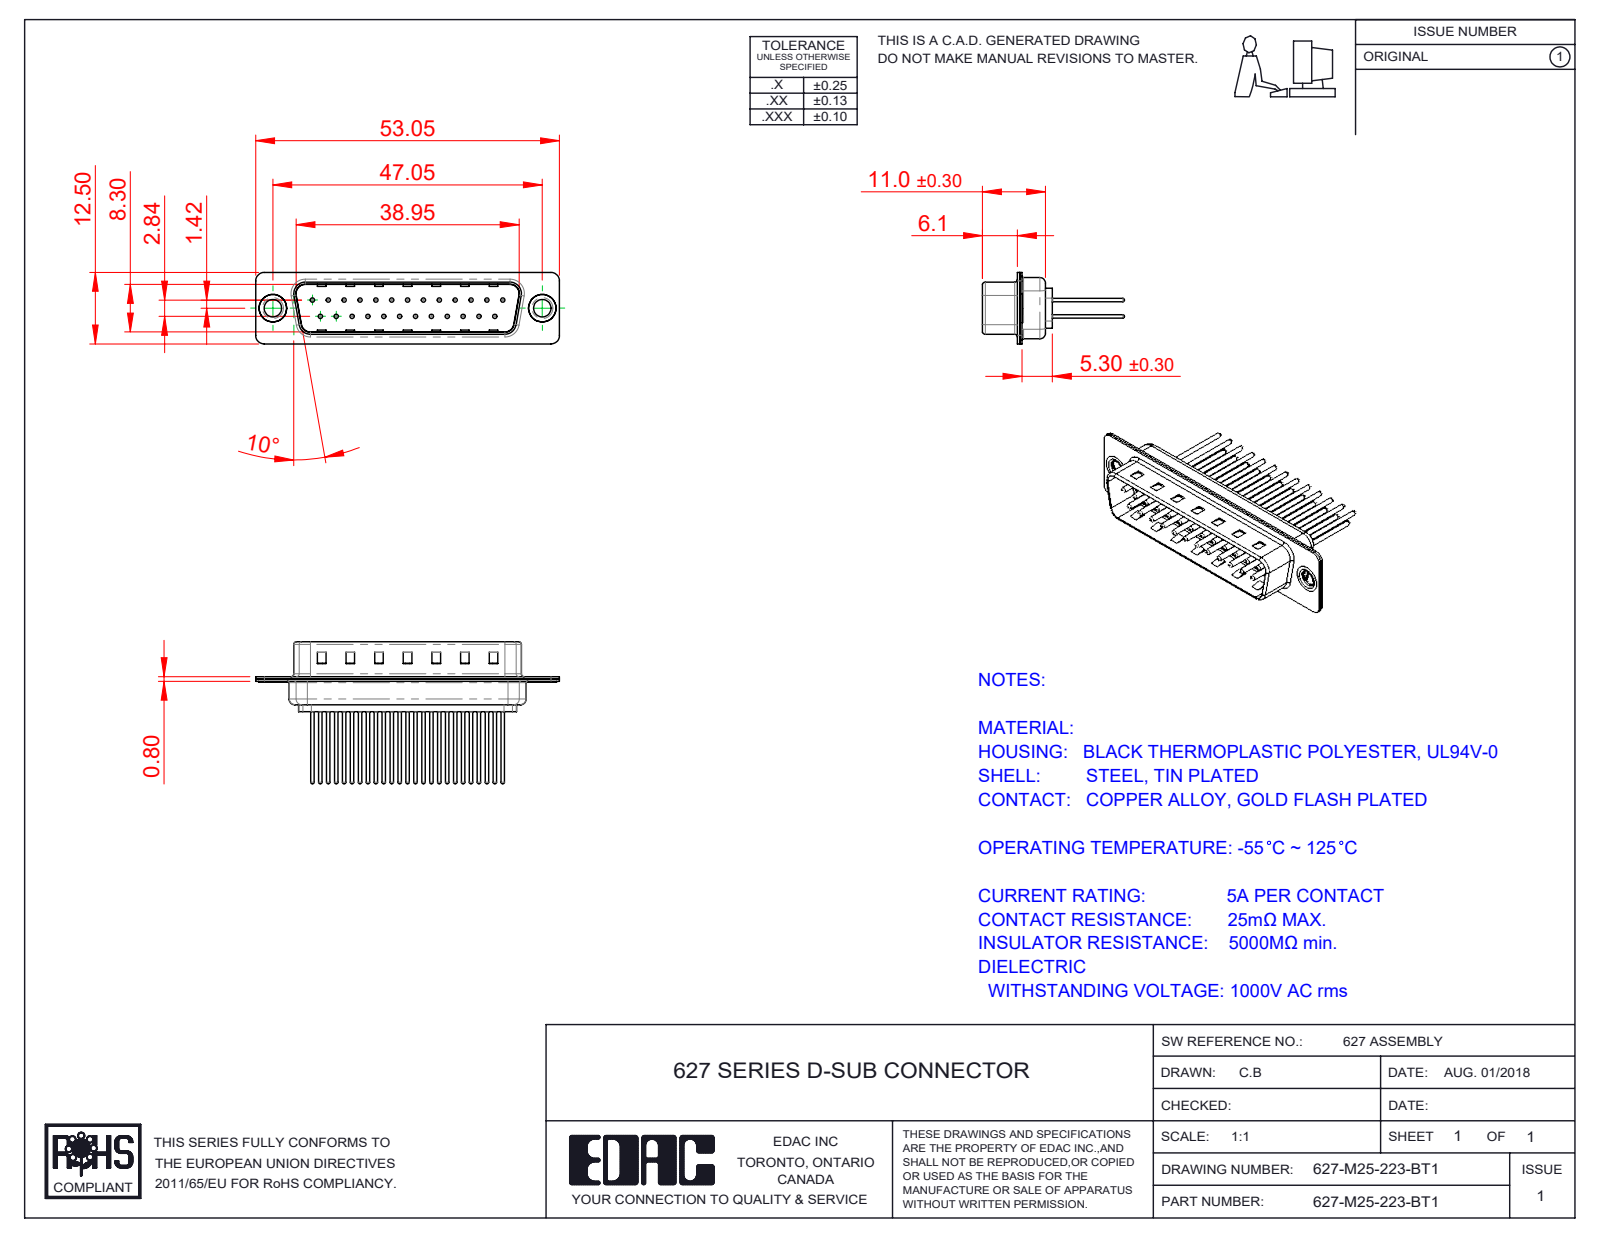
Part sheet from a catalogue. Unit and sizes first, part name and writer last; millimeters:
Units: millimetres
Overall size (bounding box): 53.05 × 24.77 × 12.5
Round holes (diameter × count): ⌀0.75 ×25, ⌀1.6 ×25, ⌀2 ×25, ⌀3.05 ×2, ⌀4 ×2, ⌀4.8 ×2
Round bosses / shafts (diameter × count): ⌀1.5 ×25, ⌀0.6 ×25, ⌀5 ×2, ⌀4.9 ×2, ⌀3.55 ×2
Partial cylindrical surfaces — rounded edges, fillets, slot ends (radius × count): R1.5 ×16, R2 ×12, R0.5 ×8, R1.6 ×8, R0.25 ×4, R0.6 ×4, R0.65 ×4, R0.9 ×4
Main face-to-face distances: 0.4, 0.8, 9.5, 9.1, 8.7, 9.9, 1.2, 6.1, 5.7, 0.75
Hole centre spacings: 3.16, 2.77, 5.54, 8.31, 11.08, 13.85, 16.62, 5.03
Volume: 2 690 mm³ · Surface area: 7 022 mm²
Bodies: 30 solids, 1275 faces (346 planar, 471 cylindrical, 458 other)
Part name (STEP PRODUCT): 627M Contact Row 1_23; 627-M25-223-BT1; 627M Shell Rear_25 Contacts; 627M Thru Hole Rivet (+3 more)
STEP written by: SolidWorks 2020 (CONFIG_CONTROL_DESIGN)
